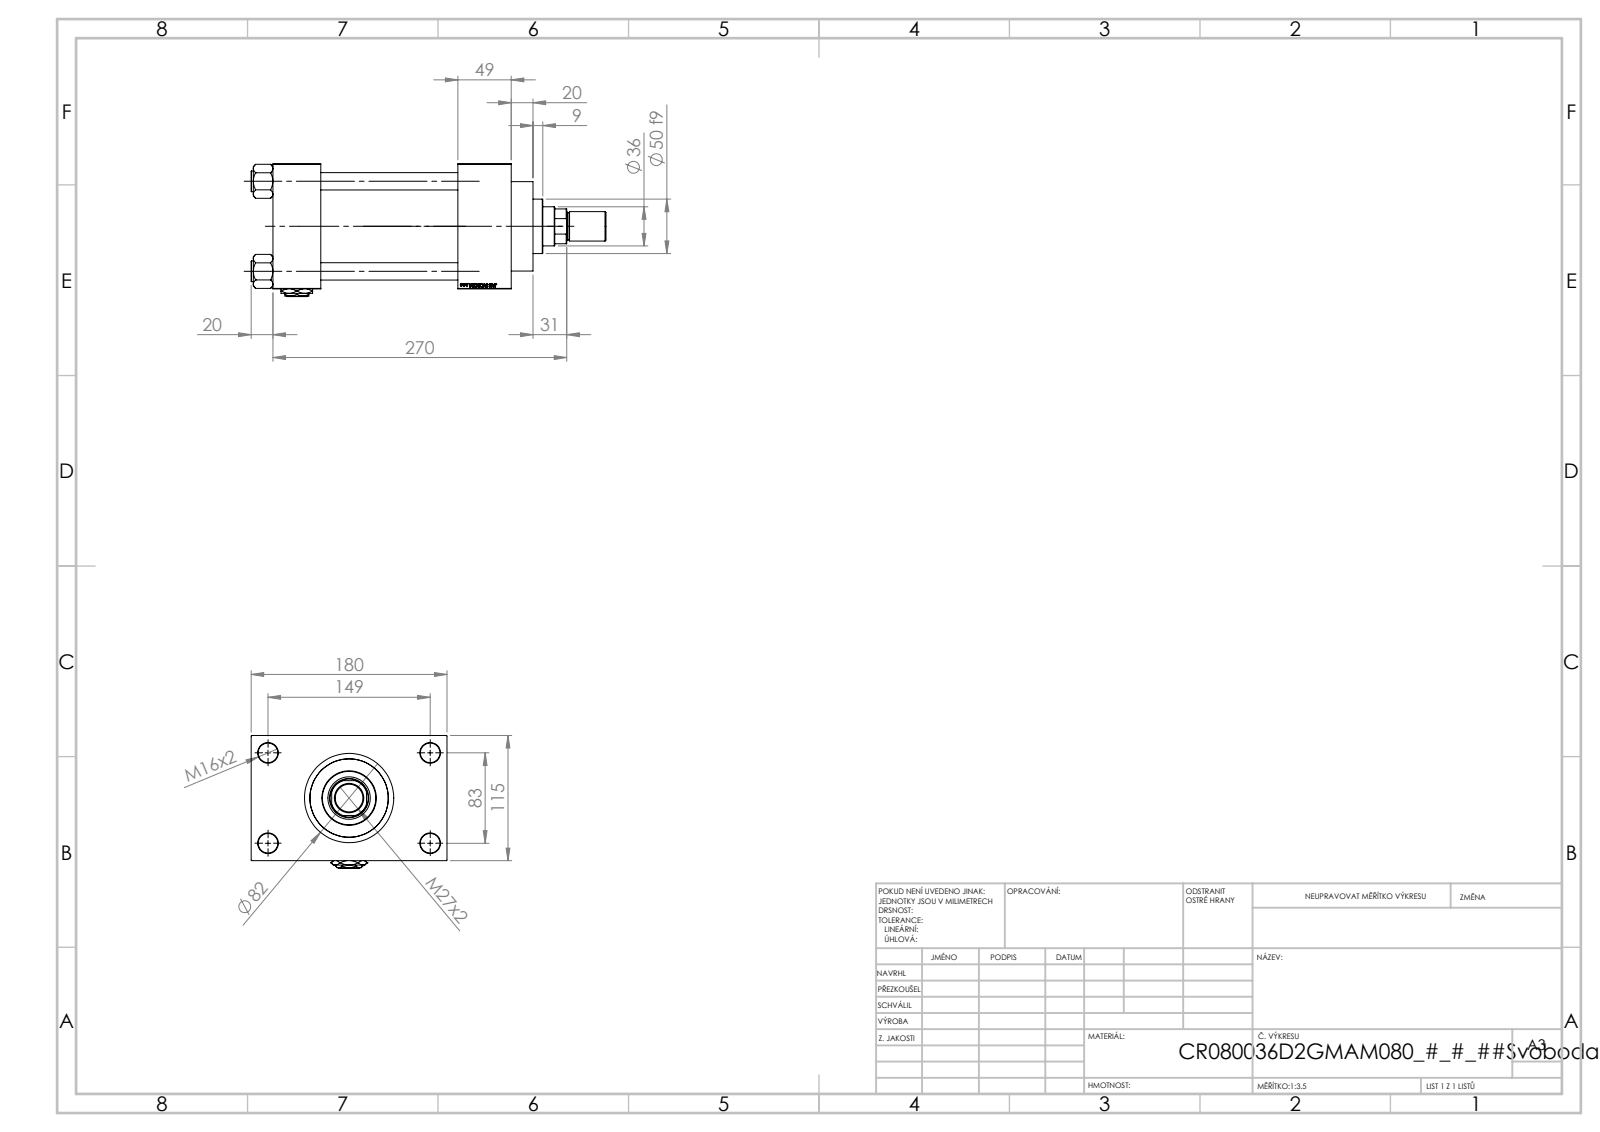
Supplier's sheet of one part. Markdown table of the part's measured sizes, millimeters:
| quantity | value |
| --- | --- |
| part name | NUT_M5_D; V215CR_D_TYCINKA; V215CR_VCP_D; Zatka_pro_OIL_PORT (+3 more) |
| STEP written by | SolidWorks 2019 (CONFIG_CONTROL_DESIGN) |
| units | millimeters |
| bodies | 13 solids, 1218 faces (573 planar, 99 cylindrical, 546 other) |
| overall size | 326 × 180 × 122 |
| volume | 2 153 000 mm³ |
| surface area | 354 640 mm² |
| round holes (diameter × count) | 16 × 4, 18 × 4, 7 × 3, 26.44 × 3, 35 × 3, 25.5 × 1, 36 × 1, 39 × 1, 61 × 1, 72 × 1, 80 × 1 |
| round bosses / shafts (diameter × count) | 19 × 4, 86 × 1, 82 × 1, 50 × 1, 27 × 1, 25 × 1 |
| partial cylindrical surfaces (radius × count) | 17.5 × 1 |
| main face-to-face distances | 115, 126, 175, 49, 170, 44, 219, 32.5, 147.5, 180 |
| hole center spacings | 33.15, 58.48, 82.7, 85.28, 89.24, 115.85, 142.43, 83 |
